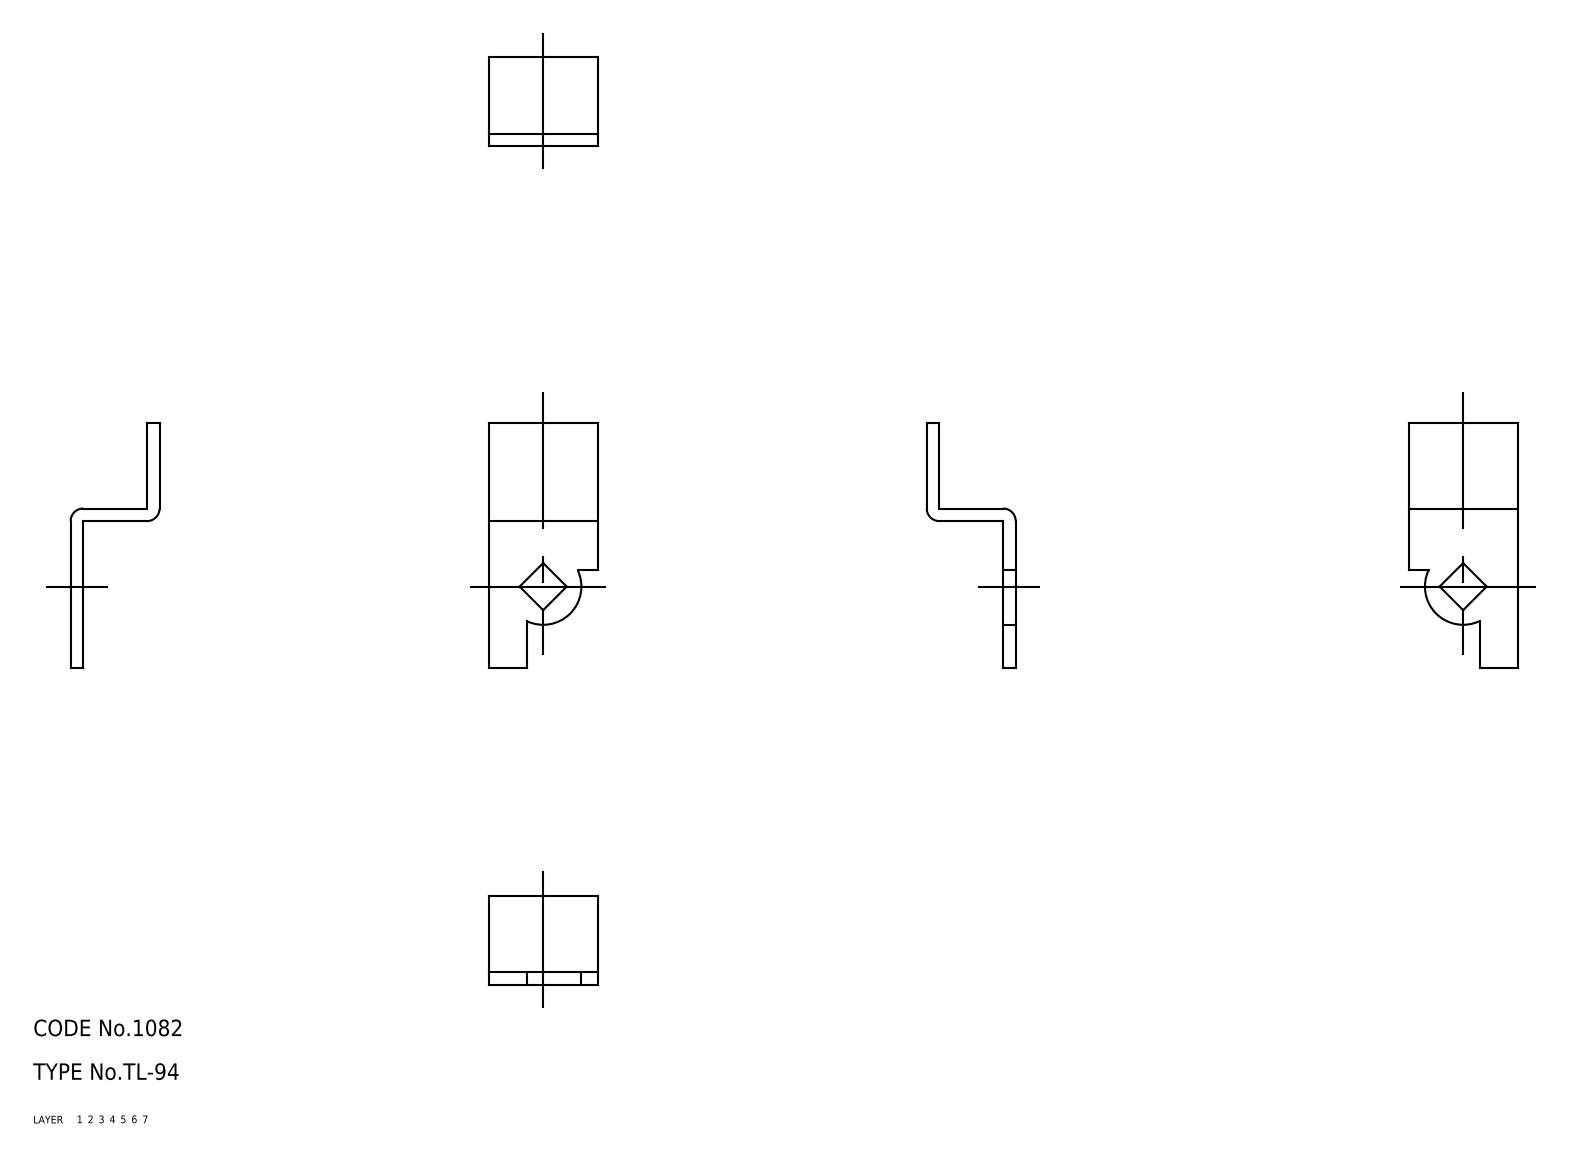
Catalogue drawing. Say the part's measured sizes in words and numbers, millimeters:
The part is named "cam". Its 3-D file was written by "CADfix (AUTOMOTIVE_DESIGN)". It is 1 solid with 19 faces: 0 planar, 0 cylindrical and 19 other. Overall it measures 45 by 20 by 16.3 millimeters. Its volume is 2 248 cubic millimeters and its surface area 2 366 square millimeters.
